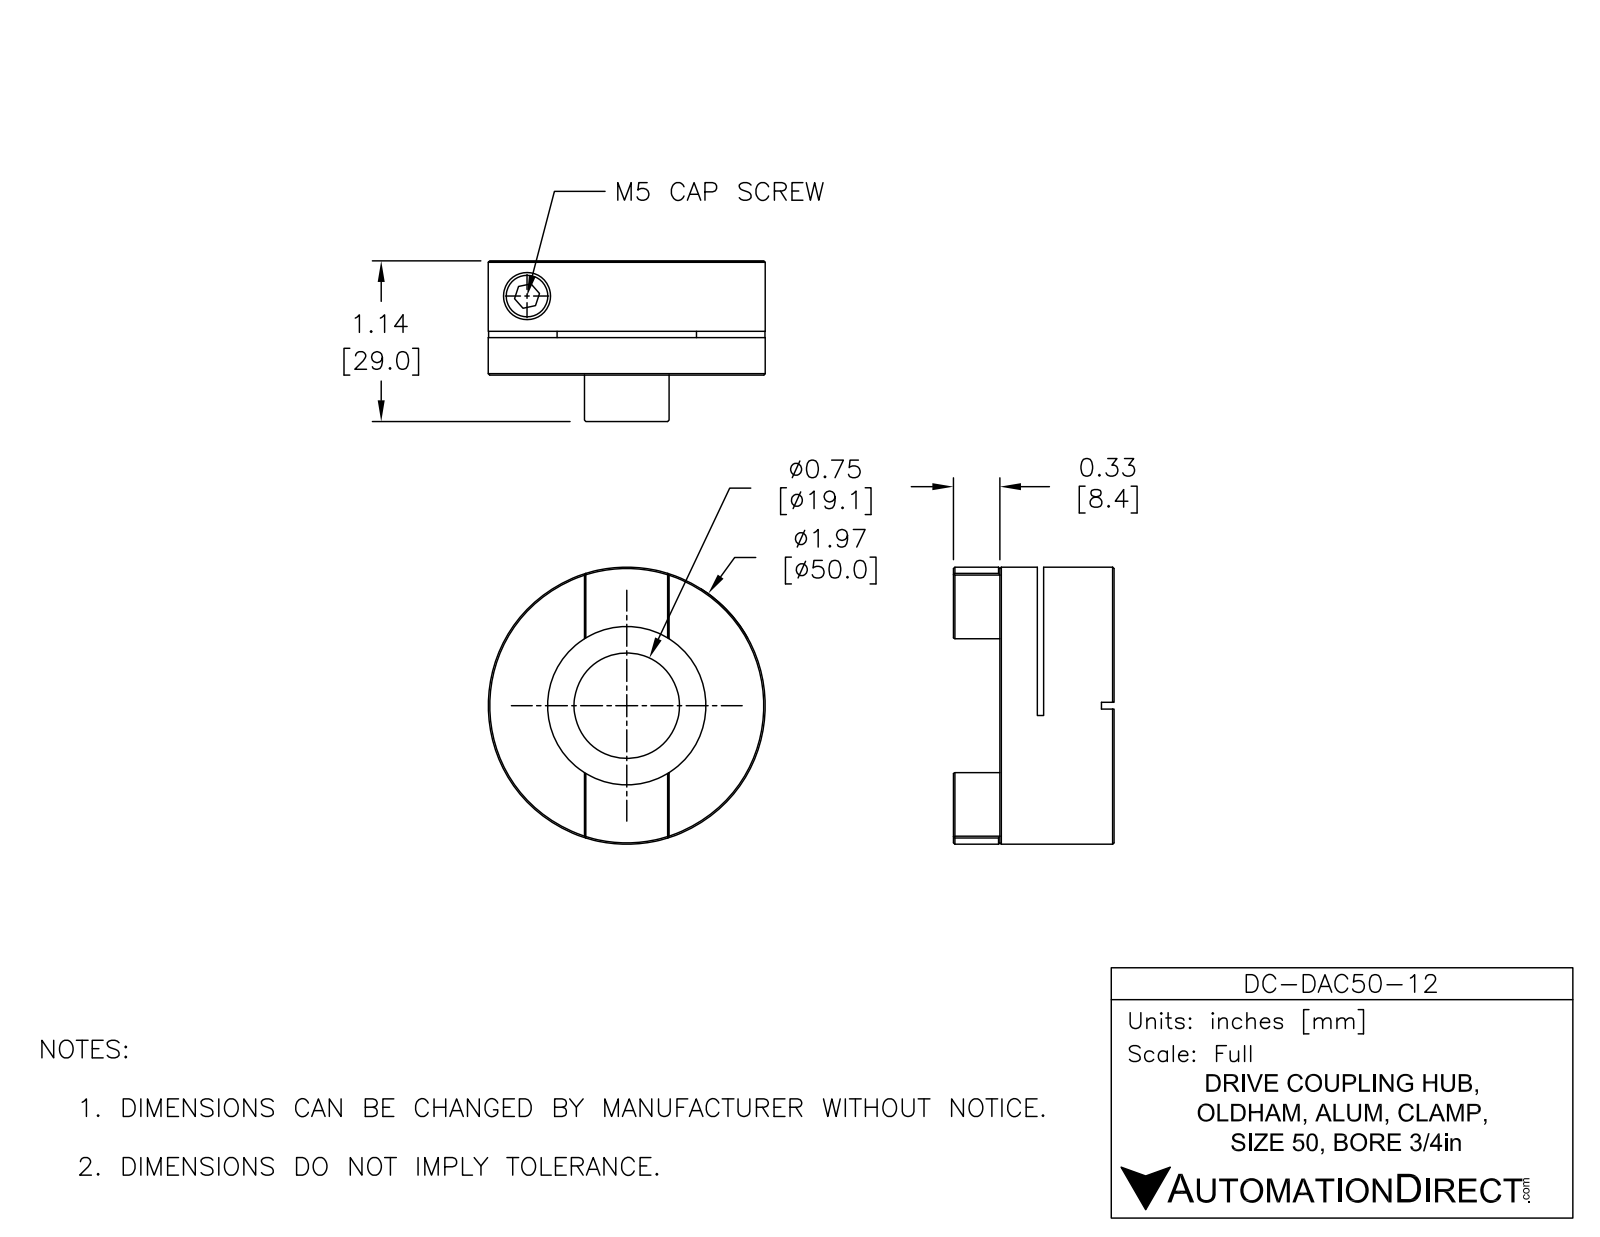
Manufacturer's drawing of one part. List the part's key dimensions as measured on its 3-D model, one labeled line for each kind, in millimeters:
Part name (STEP PRODUCT): DC-DAC50-12
STEP written by: SolidWorks 2015 (AUTOMOTIVE_DESIGN)
Units: millimetres
Bodies: 1 solid, 57 faces (30 planar, 17 cylindrical, 10 other)
Overall size (bounding box): 50 × 50 × 28.98
Volume: 33 752 mm³ · Surface area: 11 639 mm²
Round holes (diameter × count): ⌀5.51 ×1, ⌀10.01 ×1, ⌀19.05 ×1, ⌀28.58 ×1
Round bosses / shafts (diameter × count): ⌀50 ×1
Partial cylindrical surfaces — rounded edges, fillets, slot ends (radius × count): R25.4 ×1
Main face-to-face distances: 20.6, 13.84, 6.76, 12.7, 1.14, 7.9, 18.82, 6.12, 4.98, 1.78
